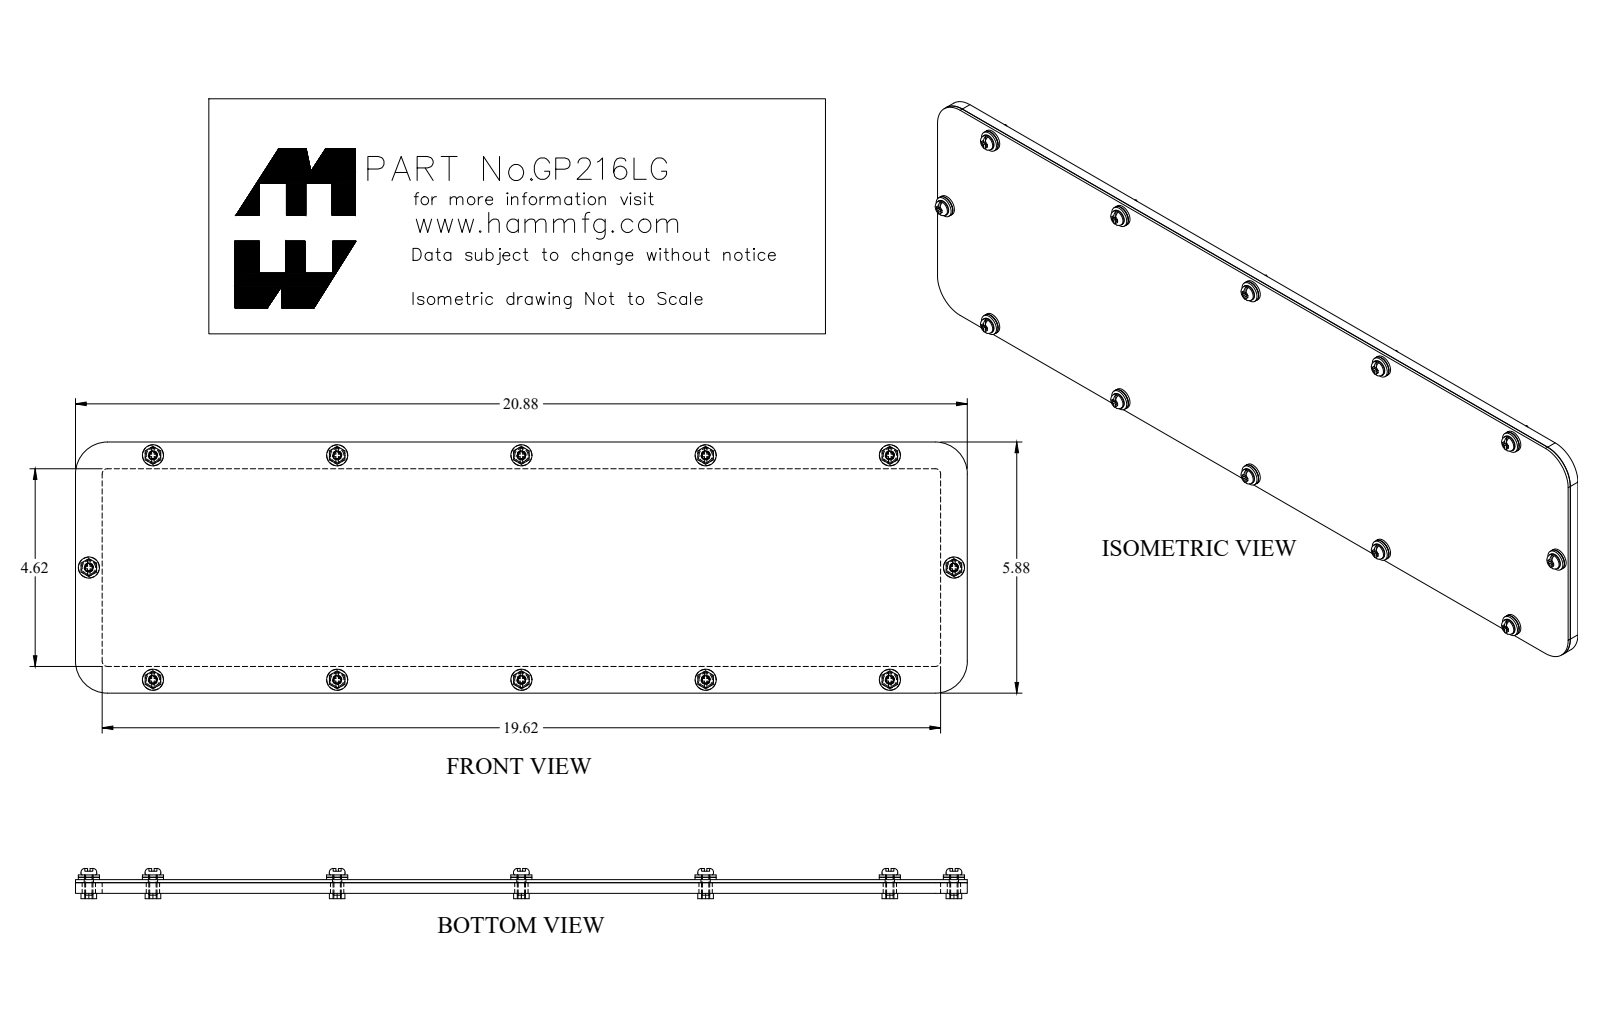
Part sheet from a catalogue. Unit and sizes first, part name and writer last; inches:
Units: inches
Overall size (bounding box): 20.875 × 5.875 × 0.707
Round holes (diameter × count): ⌀0.156 ×12, ⌀0.197 ×12, ⌀0.218 ×12, ⌀0.313 ×12
Round bosses / shafts (diameter × count): ⌀0.494 ×12, ⌀0.488 ×12, ⌀0.367 ×12, ⌀0.19 ×12
Partial cylindrical surfaces — rounded edges, fillets, slot ends (radius × count): R0.125 ×4, R0.75 ×4
Main face-to-face distances: 0.072, 0.322, 0.25, 0.625, 5.25, 5.875, 4.625, 0.11, 0.182, 0.432
Hole centre spacings: 4.312, 8.624, 6.794, 12.937, 10.097, 6.794, 10.097, 13.962
Volume: 17.05 in³ · Surface area: 356.4 in²
Bodies: 38 solids, 664 faces (364 planar, 228 cylindrical, 72 other)
Part name (STEP PRODUCT): GP216LG
STEP written by: SolidWorks 2018 (AUTOMOTIVE_DESIGN)
